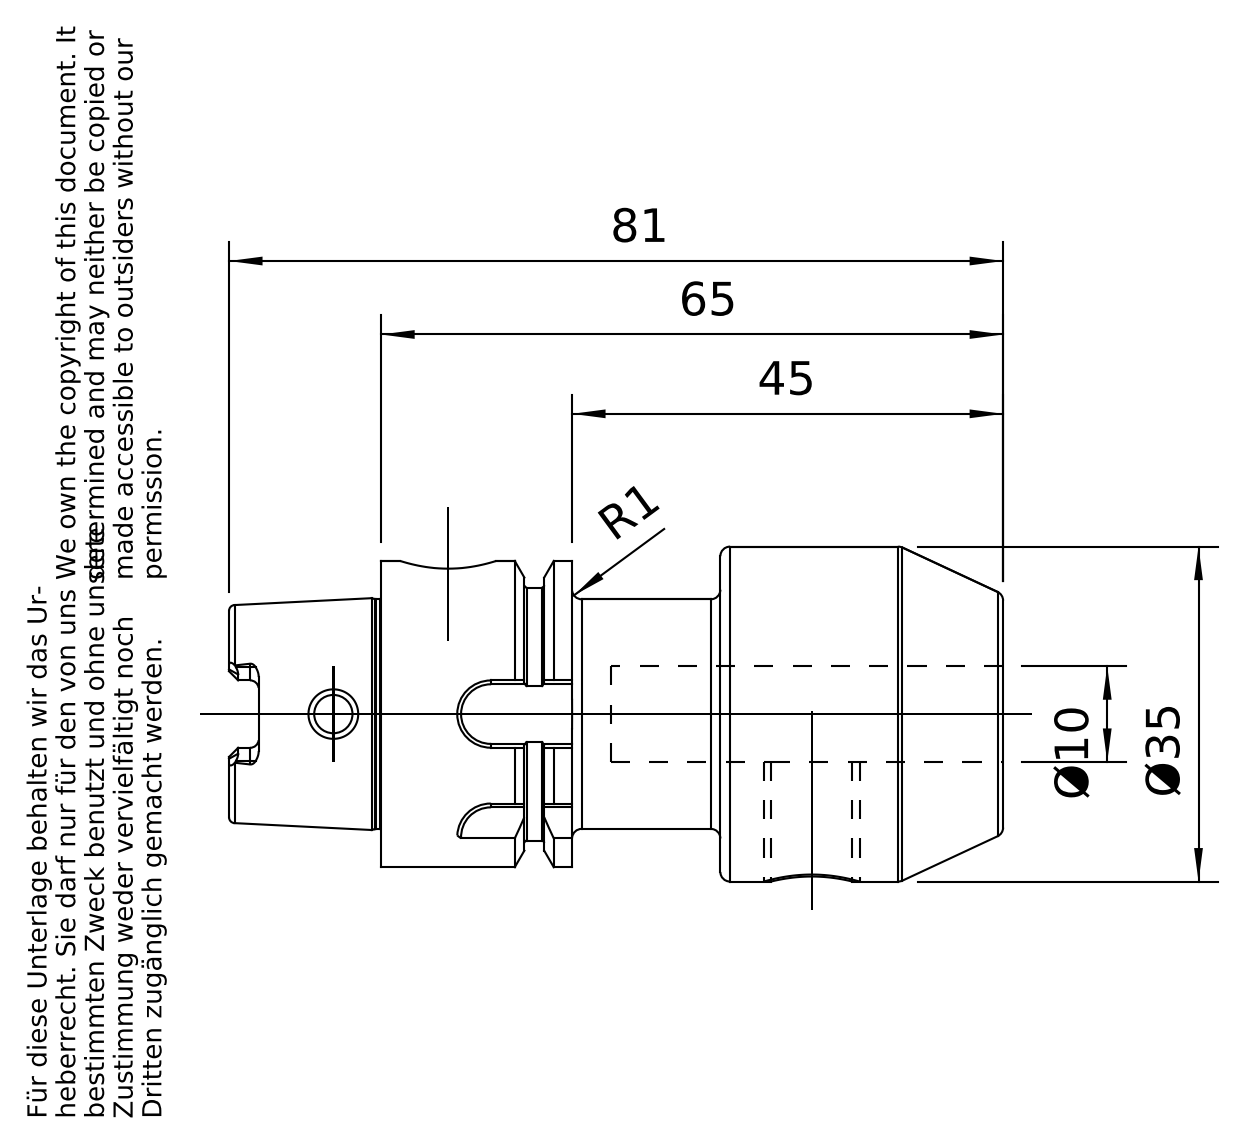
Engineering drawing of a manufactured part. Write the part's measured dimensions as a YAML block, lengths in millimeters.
part_name: "A32-000-10"
step_written_by: "PRO/ENGINEER BY PARAMETRIC TECHNOLOGY CORPORATION, 2010430 (CONFIG_CONTROL_DESIGN)"
units: millimeters
bodies: {solids: 1, faces: 196, planar: 63, cylindrical: 55, other: 78}
overall_size: [80.9, 35, 35]
volume: 43133
surface_area: 13586
round_holes:
  - {diameter: 10, count: 3}
  - {diameter: 8.5, count: 2}
  - {diameter: 4, count: 1}
  - {diameter: 10.22, count: 1}
  - {diameter: 10.5, count: 1}
  - {diameter: 17.04, count: 1}
  - {diameter: 21.07, count: 1}
round_bosses_or_shafts:
  - {diameter: 35, count: 1}
  - {diameter: 32, count: 1}
  - {diameter: 26.45, count: 1}
  - {diameter: 24.03, count: 1}
  - {diameter: 24, count: 1}
partial_cylinders:
  - {radius: 0.9, count: 6}
  - {radius: 1.38, count: 4}
  - {radius: 3.5, count: 3}
  - {radius: 3.51, count: 1}
face_to_face_distances: [29.55, 35.45, 65, 19.95, 15.5, 45.05, 6, 7.95, 12, 27.5]
hole_center_spacings: [38]
